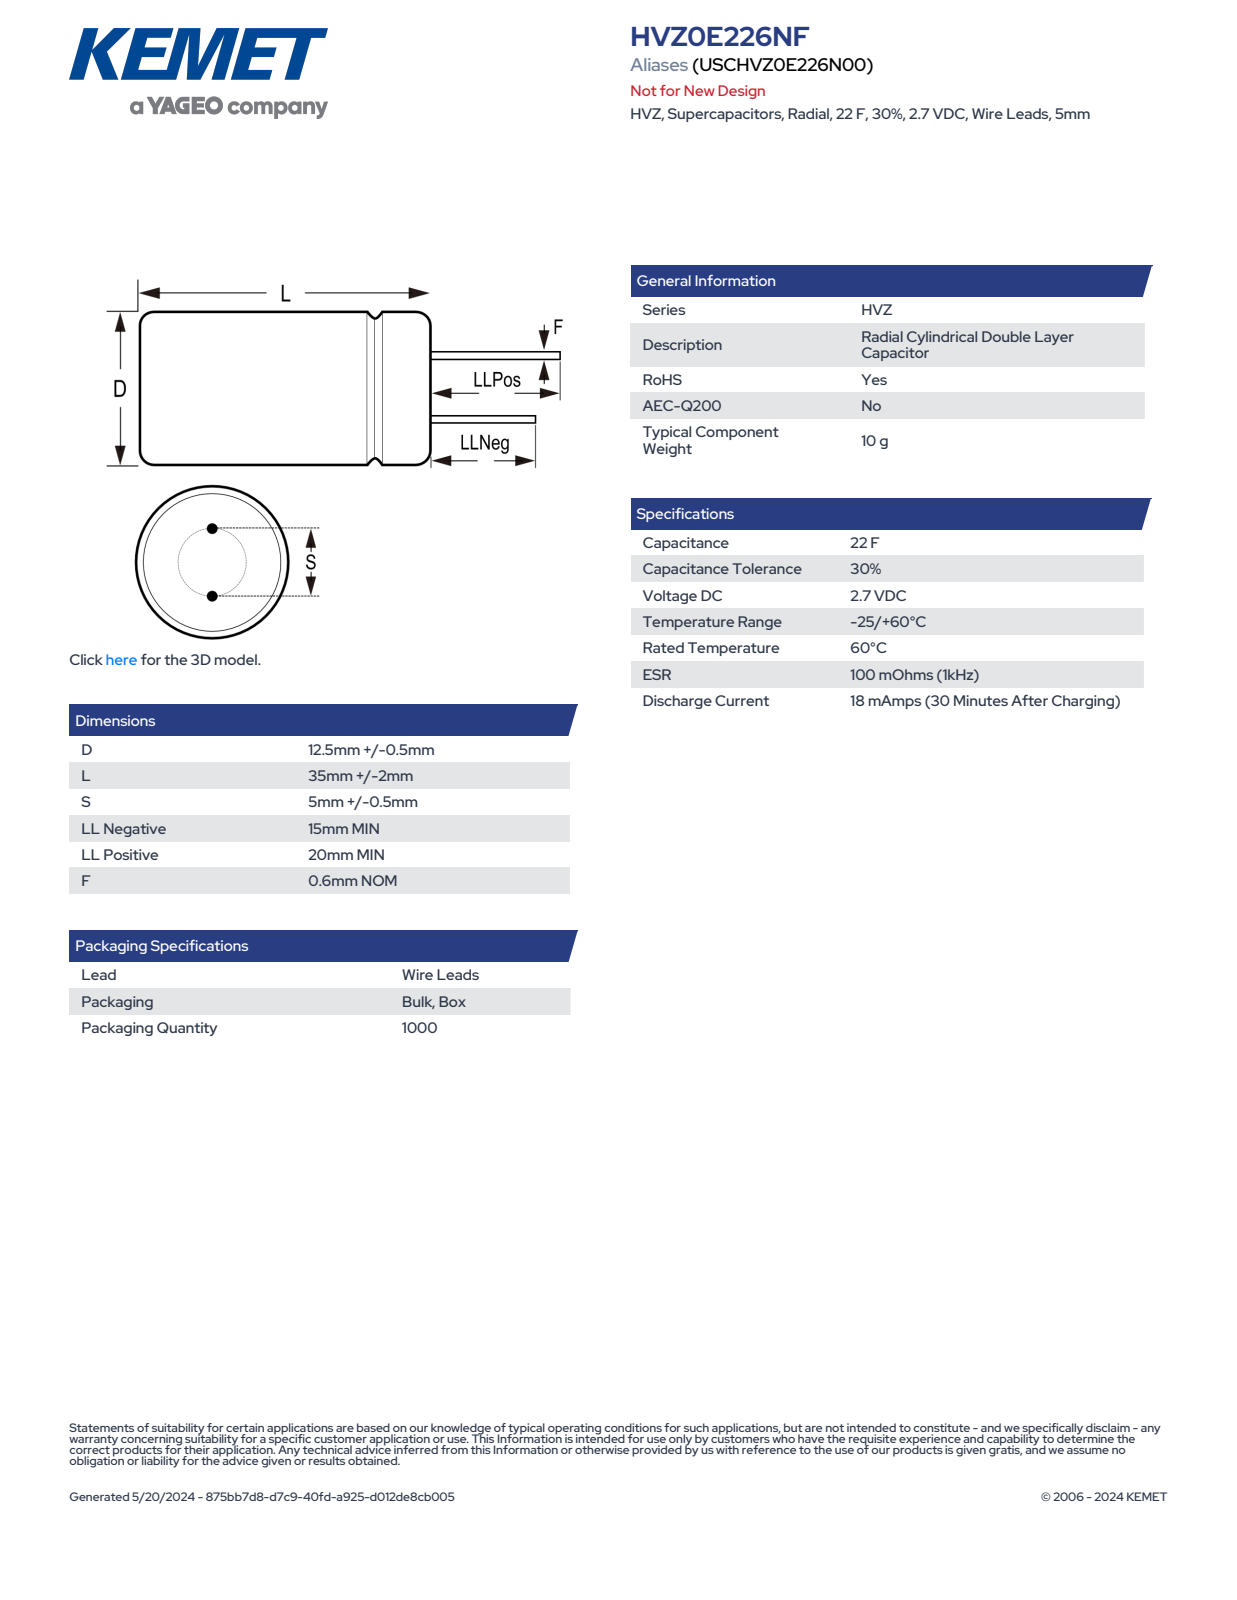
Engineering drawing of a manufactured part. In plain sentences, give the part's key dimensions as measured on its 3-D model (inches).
The part is named "CDR_CCW_D13L37S5F0.6". Its 3-D file was written by "SolidWorks 2014 (AUTOMOTIVE_DESIGN)". It is 1 solid with 82 faces: 26 planar, 17 cylindrical and 39 other. Overall it measures 2.244 by 0.512 by 0.512 inches. Its volume is 0.299 cubic inches and its surface area 2.819 square inches. Round bosses or shafts: 2 of diameter 0.024, 1 of diameter 0.512. Partial cylindrical surfaces (rounded edges, fillets, slot ends): 1 of radius 0.256. The main face-to-face distances are 1.457, 2.047, 2.244, 0.591, 0.787, 0.197.
